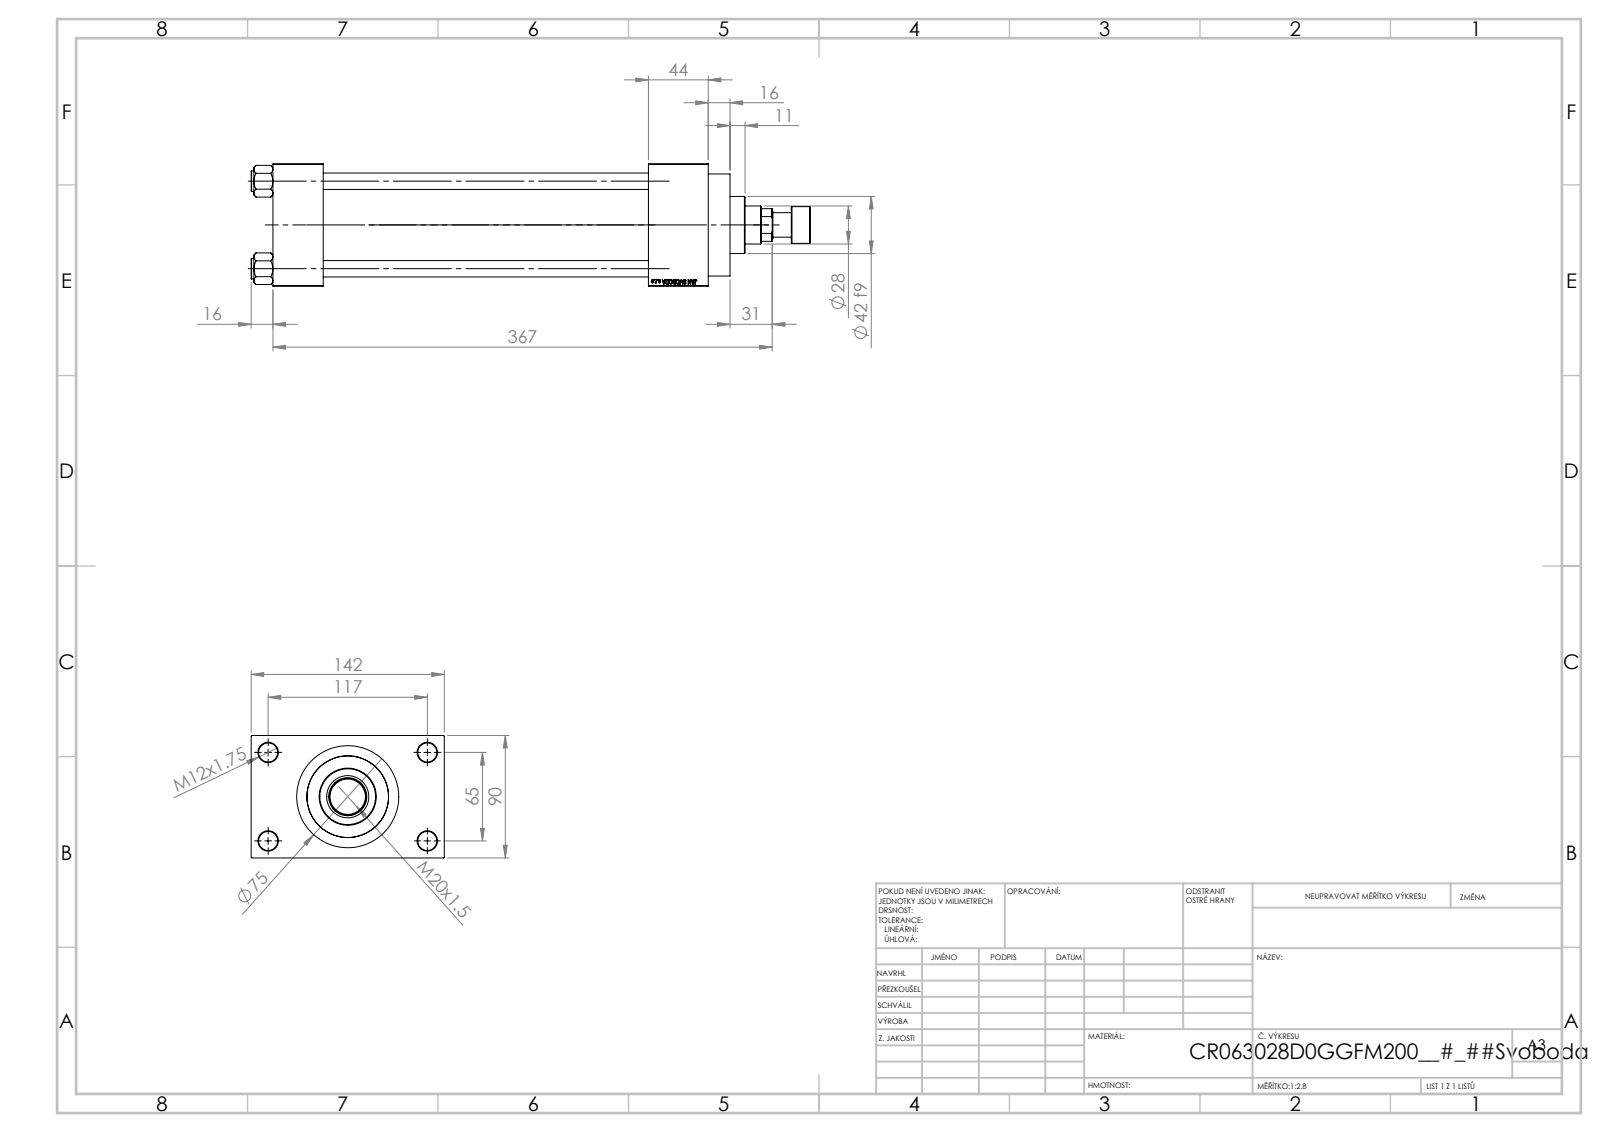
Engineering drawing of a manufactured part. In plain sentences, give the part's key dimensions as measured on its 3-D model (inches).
The part is named "V215CR_D_TYCINKA; V215CR_ROD_END_F; V215_VC_A; V215CR_VCP_D (+2 more)". Its 3-D file was written by "SolidWorks 2019 (CONFIG_CONTROL_DESIGN)". It is 12 solids with 1118 faces: 501 planar, 93 cylindrical and 524 other. Overall it measures 16.181 by 5.591 by 3.543 inches. Its volume is 86.71 cubic inches and its surface area 495.2 square inches. Round holes: 4 of diameter 0.472, 4 of diameter 0.551, 2 of diameter 0.276, 2 of diameter 0.825, 2 of diameter 1.181, 1 of diameter 0.728, 1 of diameter 1.102, 1 of diameter 1.22, 1 of diameter 1.969, 1 of diameter 2.362, 1 of diameter 2.48. Round bosses or shafts: 4 of diameter 0.591, 1 of diameter 2.953, 1 of diameter 2.717, 1 of diameter 1.654, 1 of diameter 1.063, 1 of diameter 0.709. The main face-to-face distances are 3.543, 9.409, 1.457, 10.866, 11.142, 12.598, 1.732, 1.024, 4.567, 5.591. The hole center spacings are 1.037, 1.79, 2.531, 2.635, 2.748, 3.569, 4.383, 2.559.
